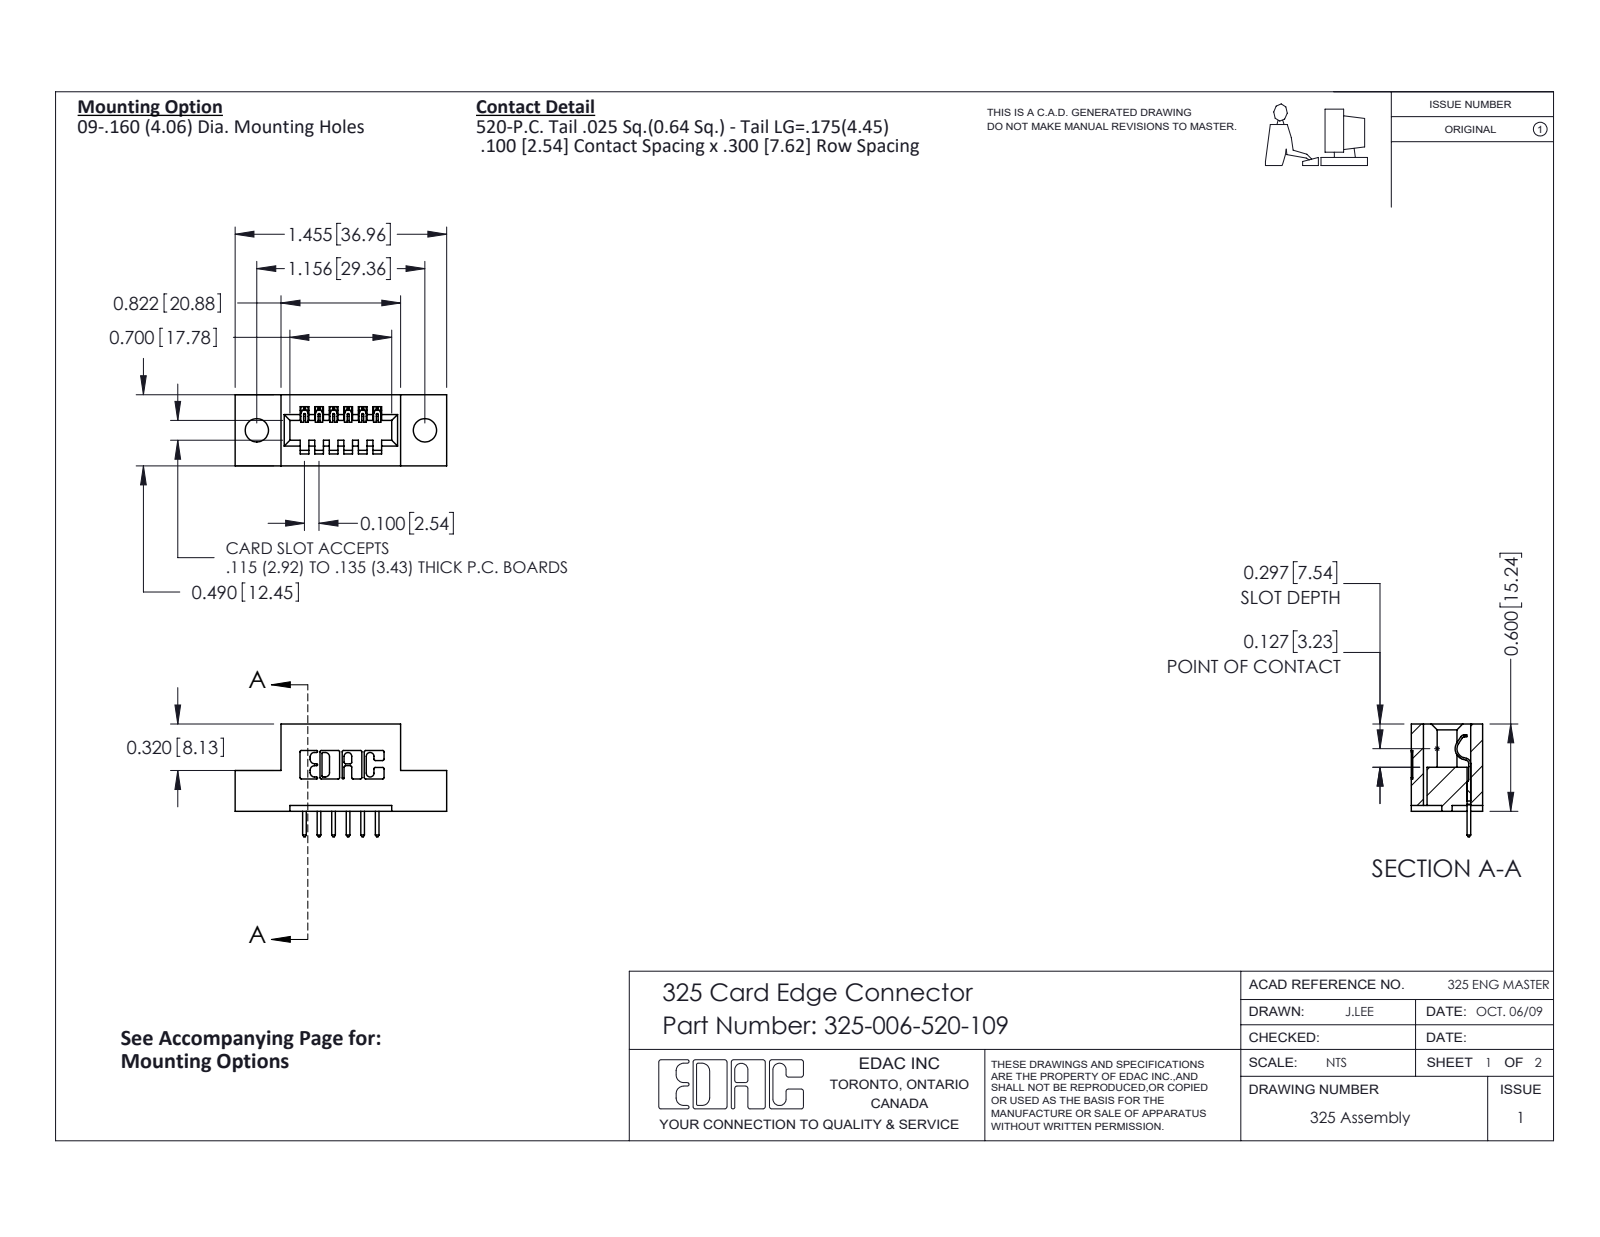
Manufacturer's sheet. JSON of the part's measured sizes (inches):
{"part_name": "325-292-001_325-293-120; 325-006-520-109; 325 Part_.160 TH", "step_written_by": "SolidWorks 2016 (CONFIG_CONTROL_DESIGN)", "units": "inches", "bodies": {"solids": 7, "faces": 462, "planar": 322, "cylindrical": 140, "other": 0}, "overall_size": [1.455, 0.775, 0.49], "volume_in3": 0.254, "surface_area_in2": 5.842, "round_holes": [[0.16, 2]], "partial_cylinders_radius": [[0.01, 22], [0.006, 12], [0.01, 12], [0.007, 6], [0.031, 6], [0.026, 3], [0.014, 1], [0.022, 1]], "face_to_face_distances": [0.1, 0.3, 0.04, 0.49, 0.2, 0.083, 0.407, 0.06, 0.16, 0.28], "hole_center_spacings": [1.156]}
